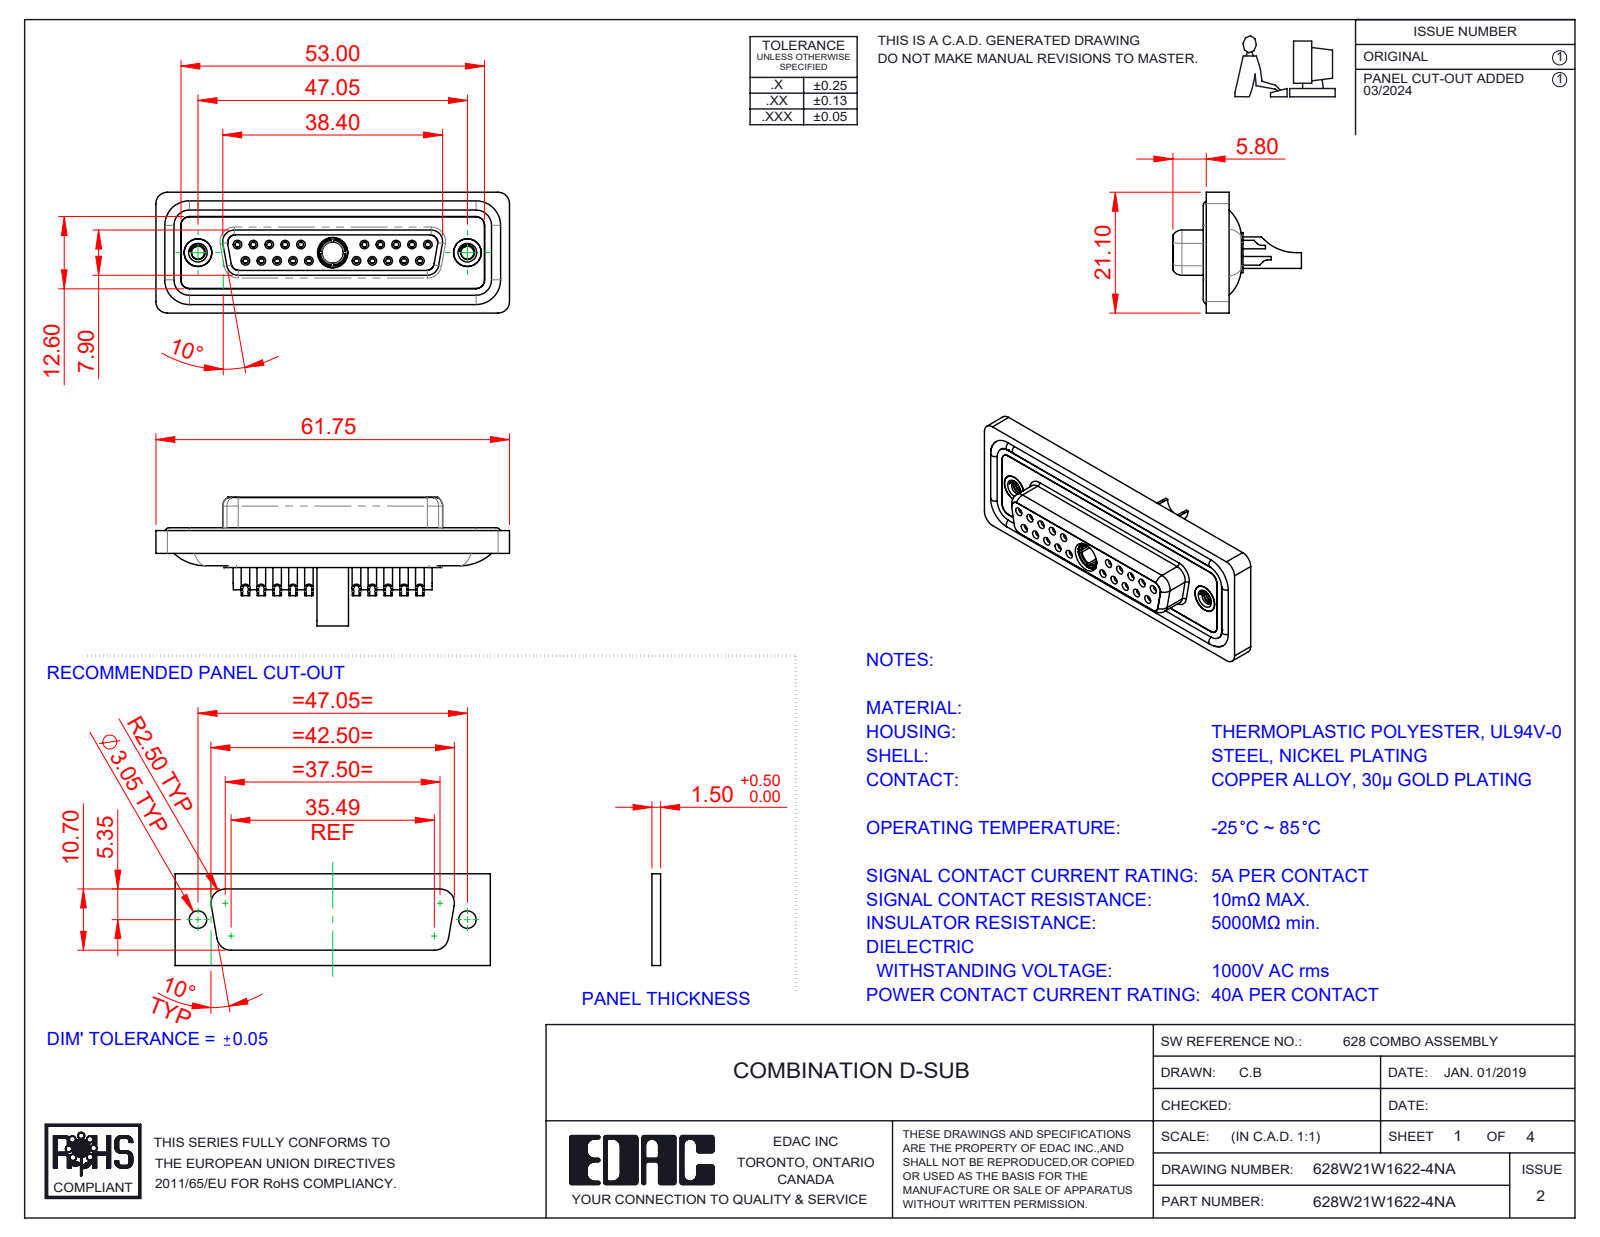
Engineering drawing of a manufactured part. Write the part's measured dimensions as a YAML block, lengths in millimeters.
part_name: "628Combo Waterproof Housing_25 Contacts; 628Combo Housing_21W1; 628Combo Threaded Rivet_A; 628Combo Contact Row 2_22 (+5 more)"
step_written_by: "SolidWorks 2023 (CONFIG_CONTROL_DESIGN)"
units: millimeters
bodies: {solids: 29, faces: 1561, planar: 476, cylindrical: 634, other: 451}
overall_size: [61.75, 22.45, 21.1]
volume: 8456
surface_area: 14349
round_holes:
  - {diameter: 0.9, count: 20}
  - {diameter: 1, count: 20}
  - {diameter: 1.1, count: 20}
  - {diameter: 1.5, count: 20}
  - {diameter: 2, count: 20}
  - {diameter: 1.6, count: 10}
  - {diameter: 1.7, count: 10}
  - {diameter: 4.85, count: 3}
  - {diameter: 2.26, count: 2}
  - {diameter: 4, count: 2}
  - {diameter: 4.05, count: 2}
  - {diameter: 5, count: 2}
round_bosses_or_shafts:
  - {diameter: 2.2, count: 20}
  - {diameter: 1.6, count: 14}
  - {diameter: 4.95, count: 2}
  - {diameter: 4.8, count: 2}
  - {diameter: 5.5, count: 1}
  - {diameter: 5.2, count: 1}
  - {diameter: 4.96, count: 1}
  - {diameter: 4.75, count: 1}
partial_cylinders:
  - {radius: 1.5, count: 22}
  - {radius: 2, count: 18}
  - {radius: 1.35, count: 8}
  - {radius: 1.6, count: 8}
  - {radius: 1, count: 6}
  - {radius: 0.25, count: 4}
  - {radius: 0.5, count: 4}
  - {radius: 0.6, count: 4}
face_to_face_distances: [0.4, 1.8, 7.45, 5.65, 6.6, 0.5, 1.6, 7.05, 2.9, 1.1]
hole_center_spacings: [3.16, 2.77, 5.54, 5.03, 8.31, 7.48, 16.62, 19.39]
